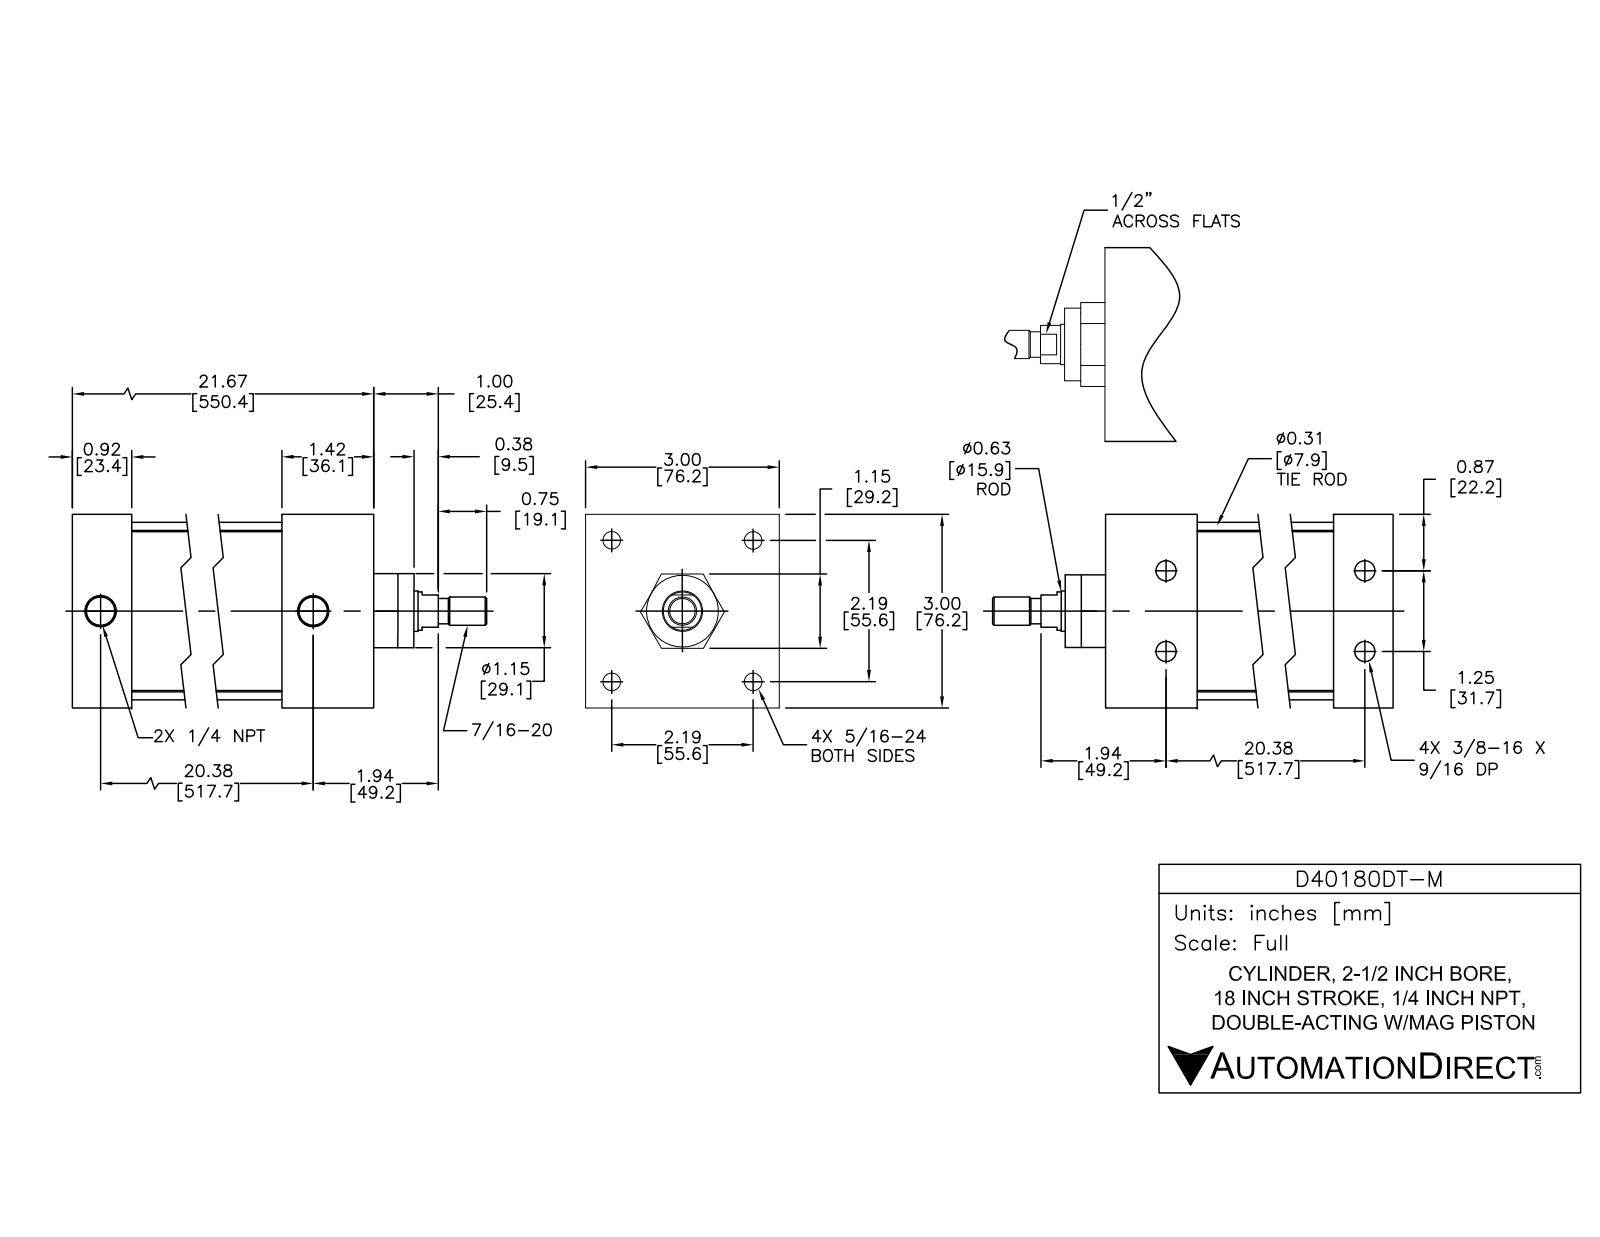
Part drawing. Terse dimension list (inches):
name: D40180DT-M BODY; D40180DT-M; D40180DT-M PISTON
written by: SolidWorks 2015 (AUTOMOTIVE_DESIGN)
unit: in
bodies: 12 solids, 298 faces (94 planar, 114 cylindrical, 90 other)
size: 23.496 × 3 × 3
volume: 57.73 in³; area: 548.5 in²
holes: 4× ⌀0.267, 4× ⌀0.307, 4× ⌀0.359, 4× ⌀0.5, 2× ⌀0.297, 2× ⌀0.477, 1× ⌀0.625, 1× ⌀0.628, 1× ⌀2.5
bosses: 4× ⌀0.484, 4× ⌀0.313, 4× ⌀0.282, 1× ⌀2.75, 1× ⌀2.497, 1× ⌀1.12, 1× ⌀0.622, 1× ⌀0.59
rounds: 4× R0.3
face distances: 3, 0.08, 19.326, 21.746, 20.726, 1.02, 1.42, 19.306, 20.326, 1
hole spacings: 1.556, 2.2, 20.379, 20.37, 0.625, 0.625, 1.25, 3.111
